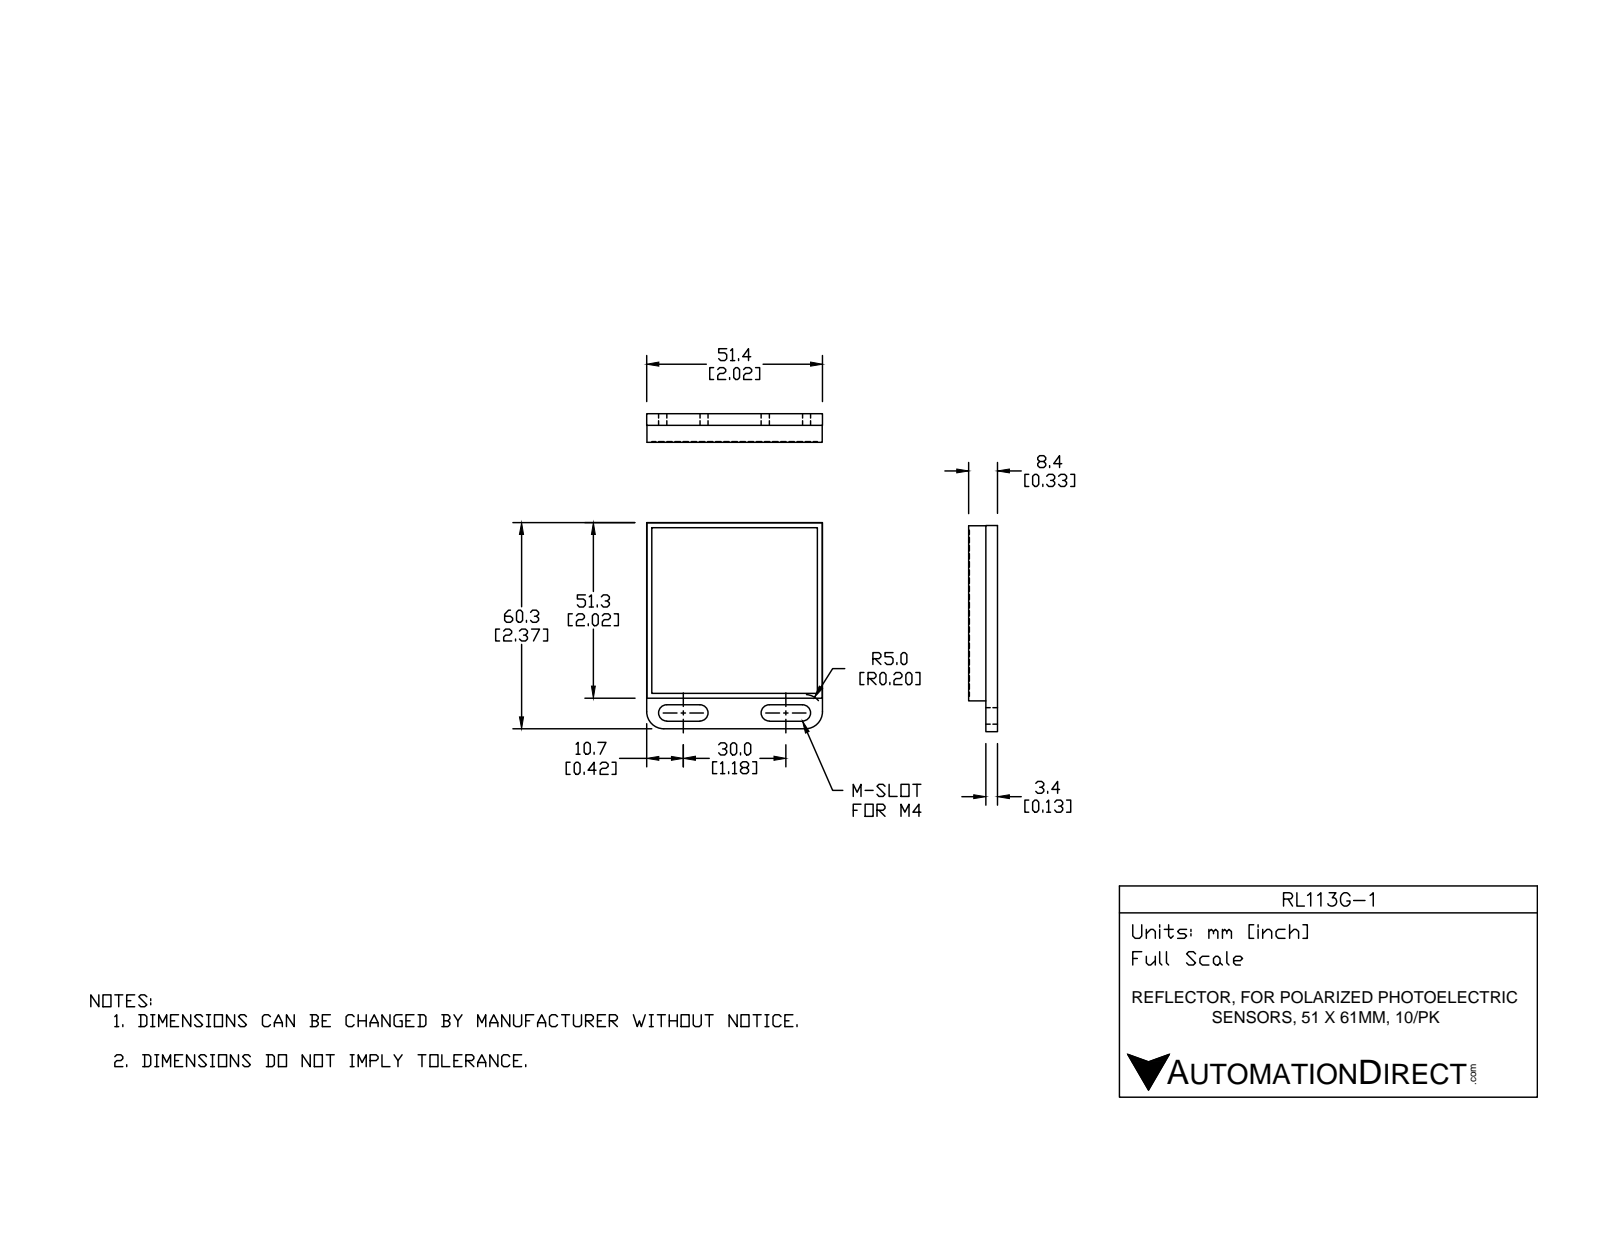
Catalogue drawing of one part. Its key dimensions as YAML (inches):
part_name: "RL-113G"
step_written_by: "SolidWorks 2017 (AUTOMOTIVE_DESIGN)"
units: inches
bodies: {solids: 1, faces: 28, planar: 20, cylindrical: 8, other: 0}
overall_size: [2.374, 2.024, 0.331]
volume: 1.387
surface_area: 12.34
partial_cylinders:
  - {radius: 0.094, count: 4}
  - {radius: 0.197, count: 2}
face_to_face_distances: [0.323, 2.021, 2.018, 0.189, 0.134, 0.331, 0.197, 2.024, 0.353, 2.371]
